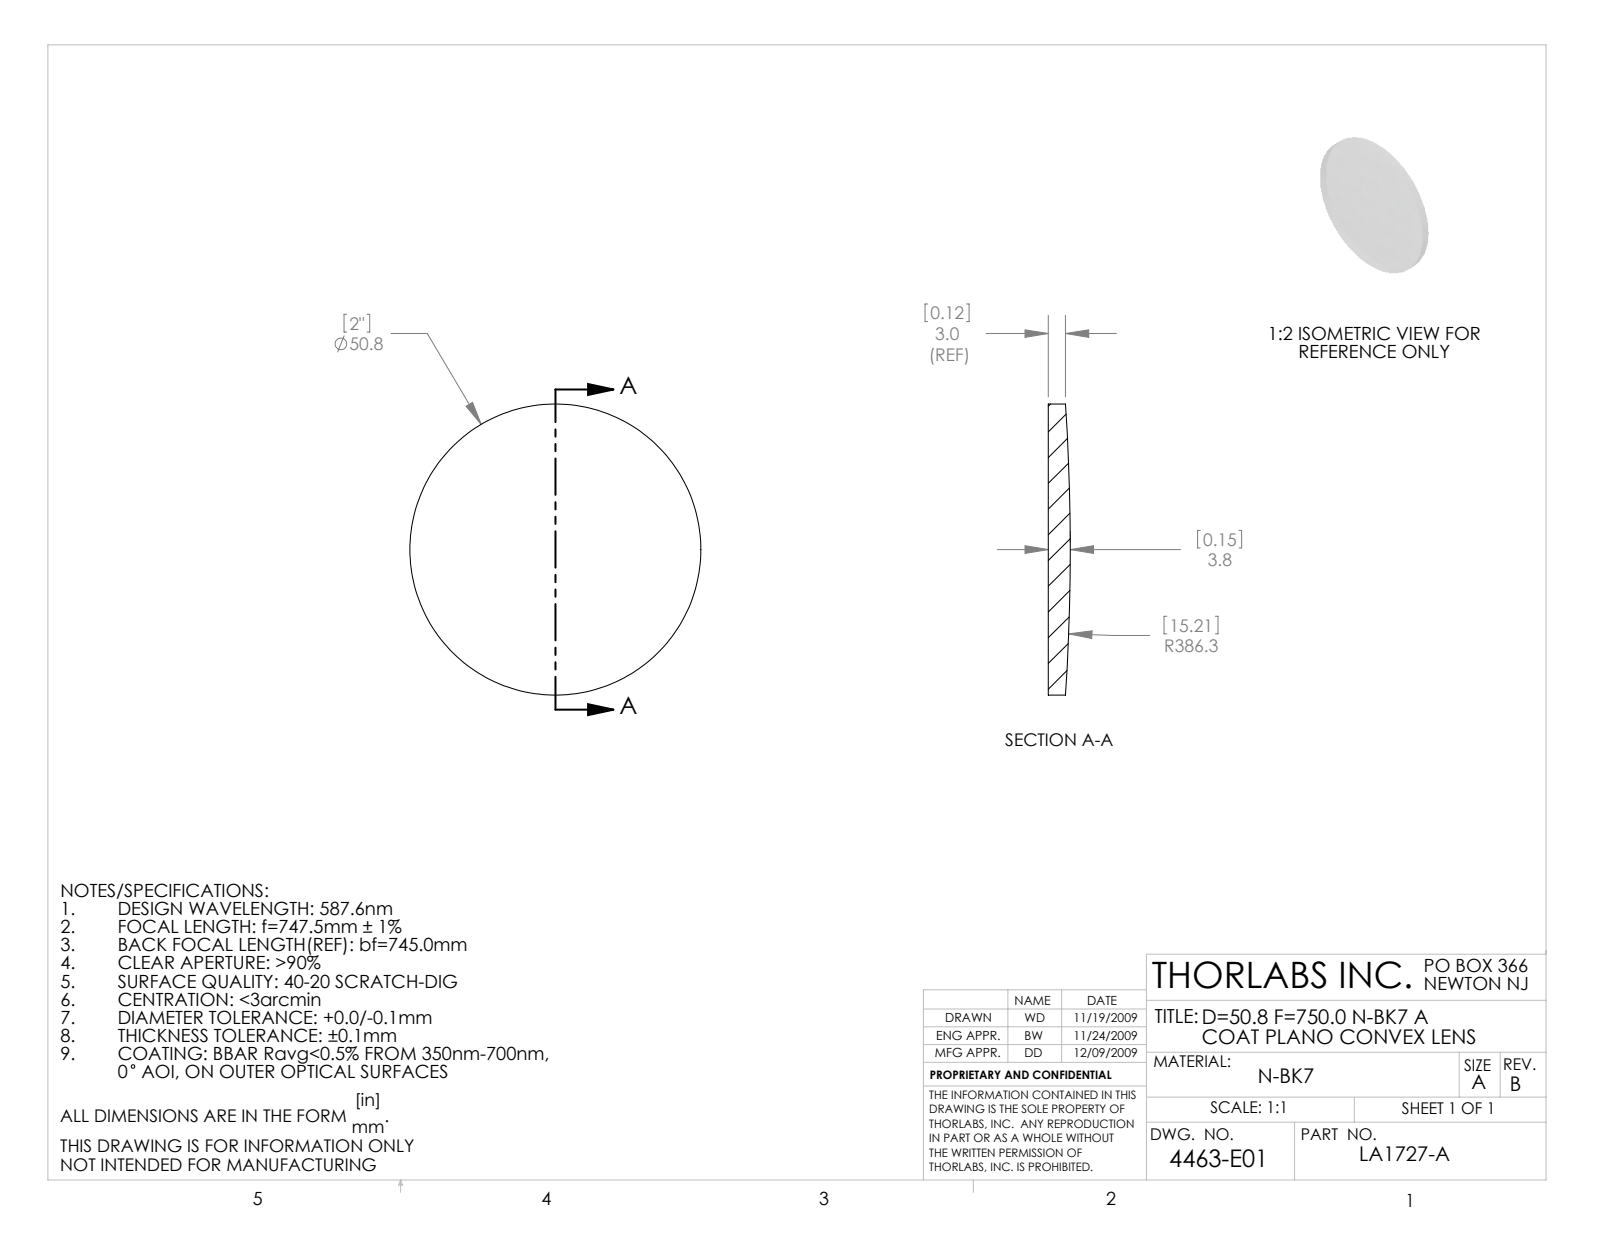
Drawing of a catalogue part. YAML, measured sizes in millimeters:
part_name: "4463-E0W"
step_written_by: "SolidWorks 2009 (AUTOMOTIVE_DESIGN)"
units: millimeters
bodies: {solids: 1, faces: 5, planar: 1, cylindrical: 2, other: 2}
overall_size: [50.8, 50.8, 3.83]
volume: 6916
surface_area: 4534
round_bosses_or_shafts:
  - {diameter: 50.8, count: 1}
